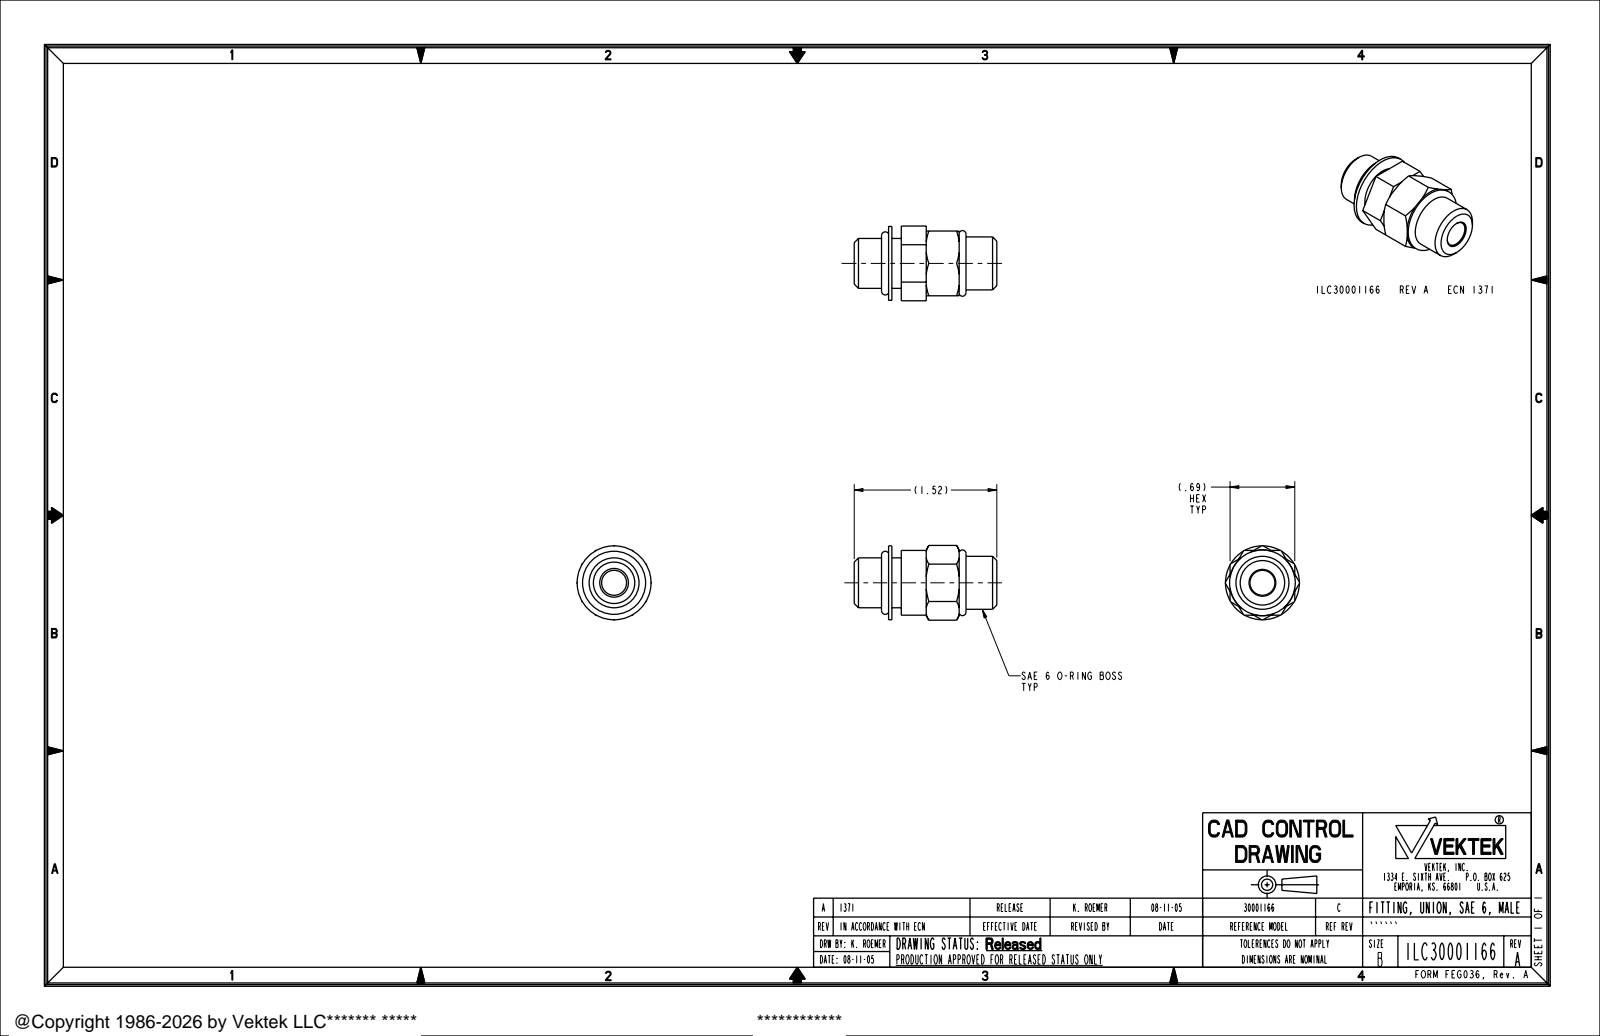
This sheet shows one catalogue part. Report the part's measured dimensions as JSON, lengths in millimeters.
{"part_name": "ILC30001166", "step_written_by": "PRO/ENGINEER BY PARAMETRIC TECHNOLOGY CORPORATION, 2004290 (AUTOMOTIVE_DESIGN_CC2)", "units": "millimeters", "bodies": {"solids": 1, "faces": 74, "planar": 32, "cylindrical": 14, "other": 28}, "overall_size": [38.5, 20.2, 20.2], "volume_mm3": 6550, "surface_area_mm2": 3730, "round_holes": [[6.7, 1]], "round_bosses_or_shafts": [[19.9, 1], [14.3, 1], [13.5, 1]], "face_to_face_distances": [17.4, 10.2, 0.9, 28.3, 2.5, 3.4, 19.1, 9.3, 25.8, 29.2]}
